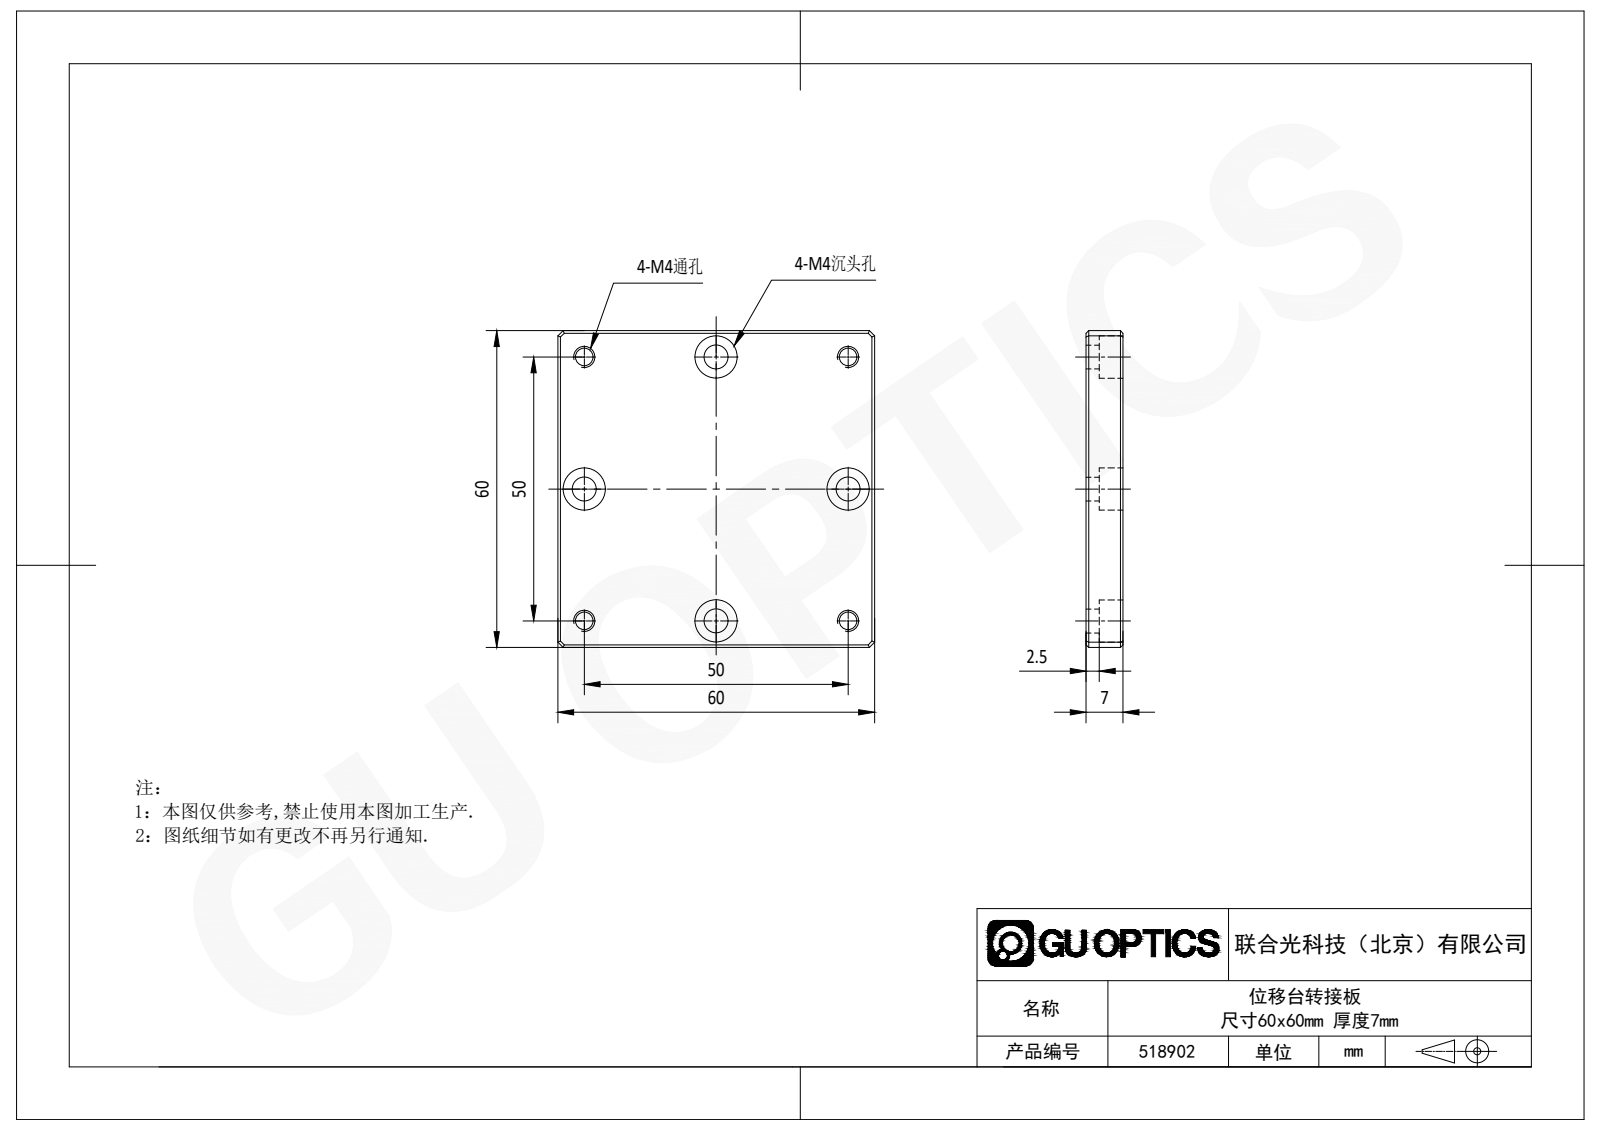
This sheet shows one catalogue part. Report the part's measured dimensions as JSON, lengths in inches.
{"step_written_by": "SolidWorks 2020 (CONFIG_CONTROL_DESIGN)", "units": "inches", "bodies": {"solids": 1, "faces": 46, "planar": 30, "cylindrical": 12, "other": 4}, "overall_size": [2.362, 2.362, 0.276], "volume_in3": 1.453, "surface_area_in2": 14.58, "round_holes": [[0.13, 4], [0.177, 4], [0.315, 4]], "face_to_face_distances": [0.276, 2.362, 1.837, 0.094, 0.181, 3.284, 2.49], "hole_center_spacings": [0.984, 2.201, 1.969, 1.392, 2.784]}
